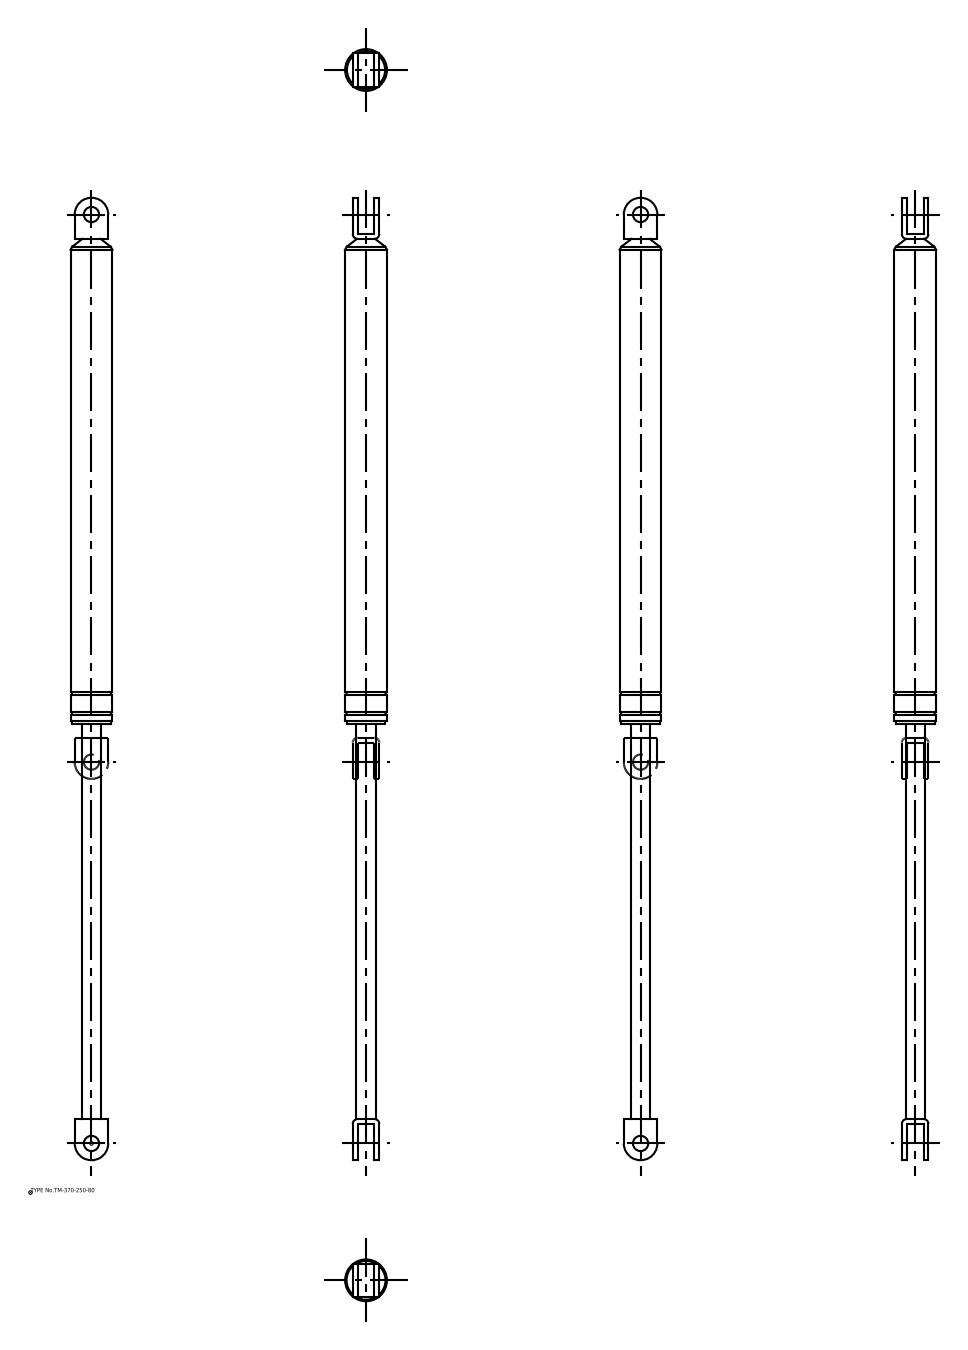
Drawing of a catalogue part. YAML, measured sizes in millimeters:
part_name: "TM_370_250_80; TM_370_250_80_div"
step_written_by: "spGate 16.7.1 (AUTOMOTIVE_DESIGN)"
units: millimeters
bodies: {solids: 2, faces: 64, planar: 22, cylindrical: 32, other: 10}
overall_size: [631, 28.2, 28.2]
volume: 224999
surface_area: 44325
round_holes:
  - {diameter: 10, count: 2}
round_bosses_or_shafts:
  - {diameter: 28.2, count: 1}
  - {diameter: 27.4, count: 1}
  - {diameter: 25.5, count: 1}
  - {diameter: 12.5, count: 1}
partial_cylinders:
  - {radius: 3.2, count: 4}
  - {radius: 11, count: 2}
face_to_face_distances: [3.2, 14.2, 17.4, 11, 22, 580.2, 262.2, 583.4, 321.2, 318]
hole_center_spacings: [609]
